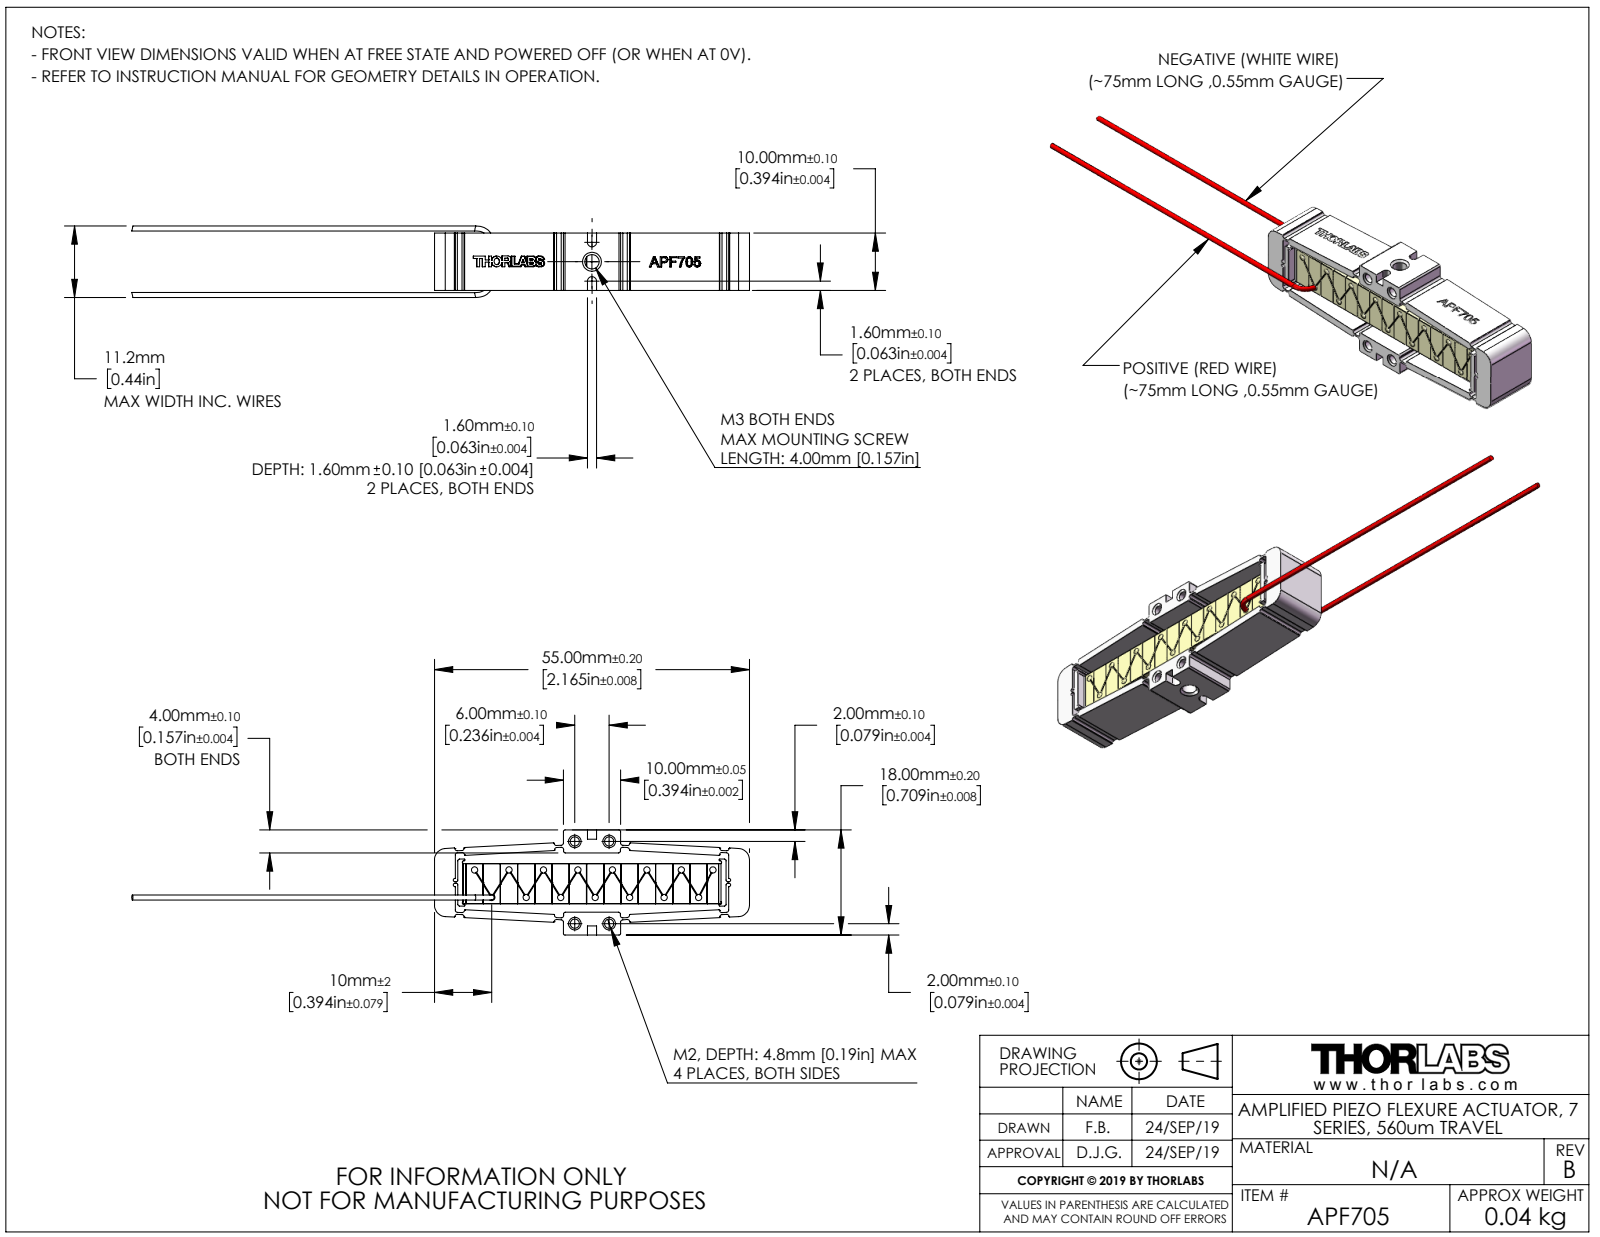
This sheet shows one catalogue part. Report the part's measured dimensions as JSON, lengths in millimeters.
{"part_name": "APF705", "step_written_by": "SolidWorks 2016 (CONFIG_CONTROL_DESIGN)", "units": "millimeters", "bodies": {"solids": 0, "faces": 683, "planar": 311, "cylindrical": 213, "other": 159}, "overall_size": [107.86, 18, 12.48], "round_holes": [[1.6, 4], [1.87, 1], [2.5, 1]], "round_bosses_or_shafts": [[1.1, 12]], "partial_cylinders_radius": [[0.4, 32], [0.1, 20], [0.3, 20], [0.15, 4], [0.23, 4], [2, 4], [0.55, 3], [0.8, 2]], "face_to_face_distances": [7, 1.37, 8.5, 1.5, 10, 12.76, 12.75, 14.13, 0.9, 3.63], "hole_center_spacings": [6, 14, 15.23]}
